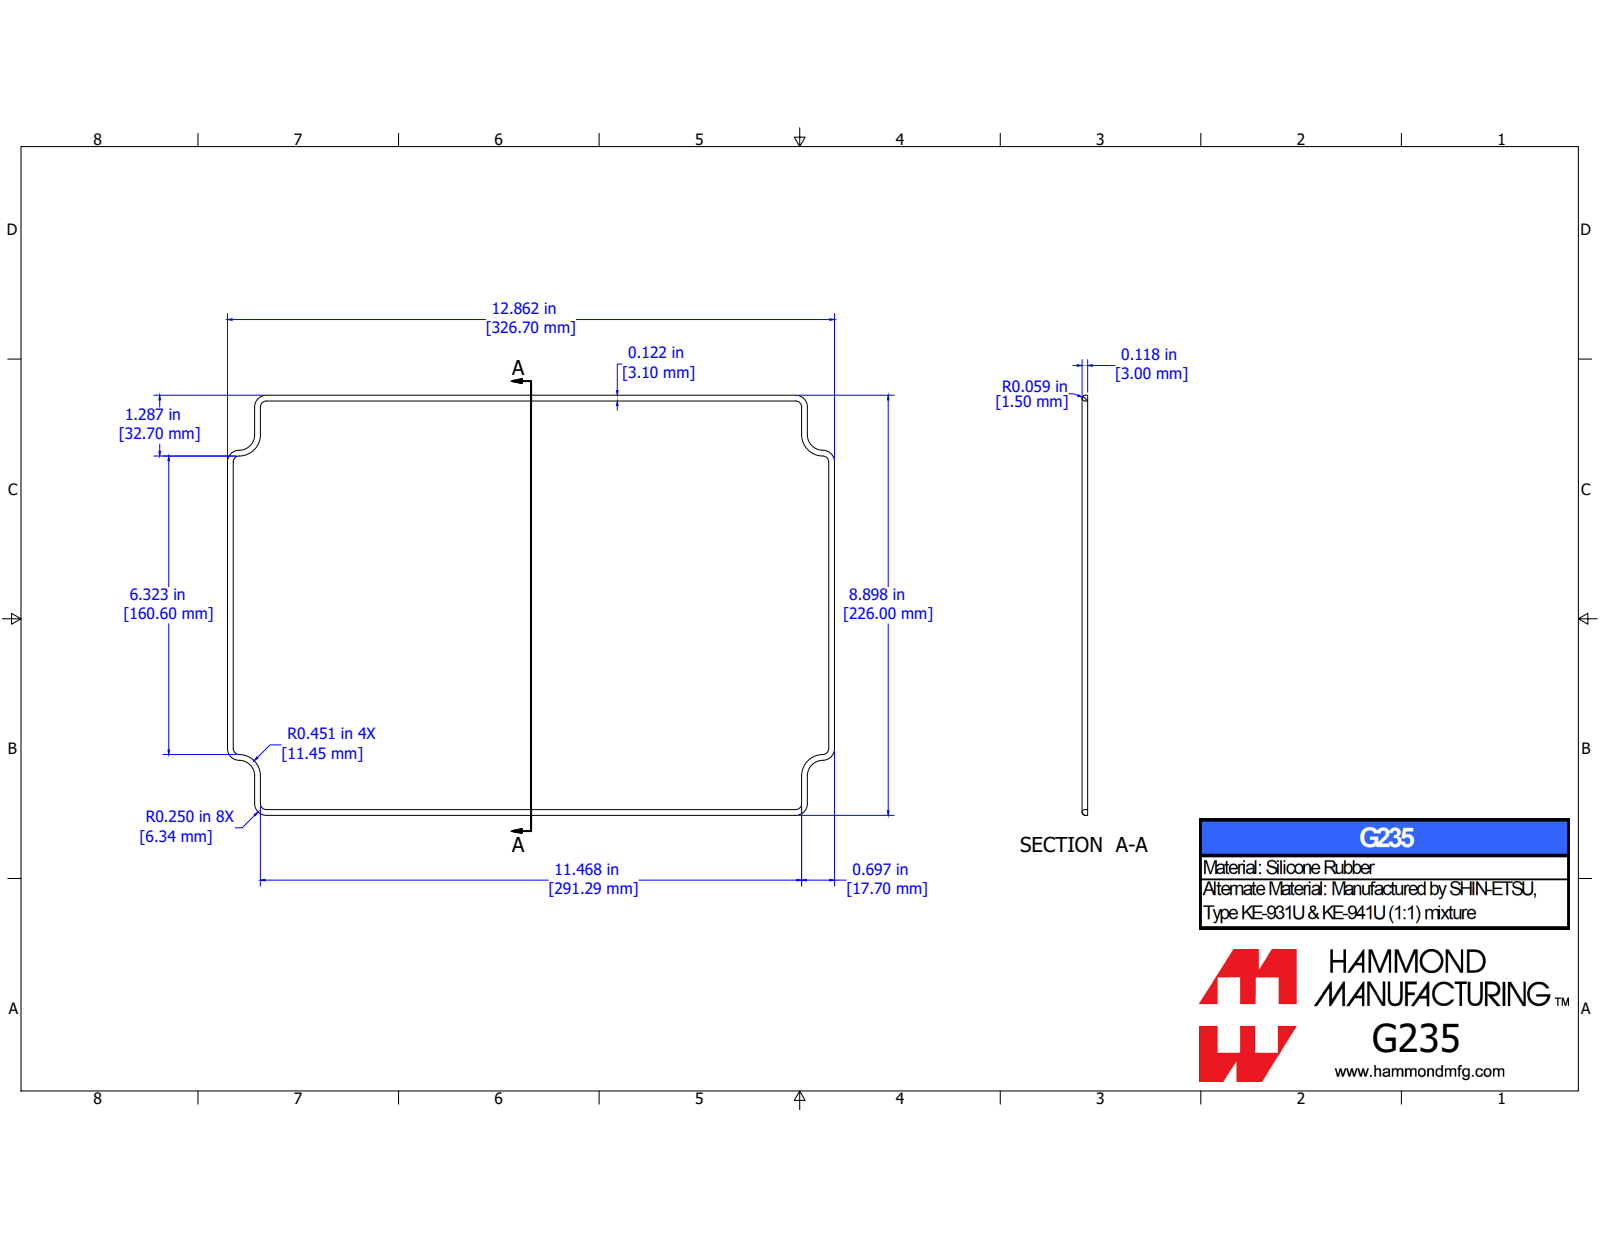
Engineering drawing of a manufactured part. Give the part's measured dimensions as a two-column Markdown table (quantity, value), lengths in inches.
| quantity | value |
| --- | --- |
| part name | 1590Z235G |
| STEP written by | SolidWorks 2019 (CONFIG_CONTROL_DESIGN) |
| units | inches |
| bodies | 1 solid, 98 faces (26 planar, 24 cylindrical, 48 other) |
| overall size | 12.85 × 8.917 × 0.138 |
| volume | 0.744 in³ |
| surface area | 21.5 in² |
| partial cylindrical surfaces (radius × count) | 0.039 × 16 |
| main face-to-face distances | 8.737, 0.138, 12.654, 0.606, 12.048, 11.442, 1.2, 7.537, 6.337 |
